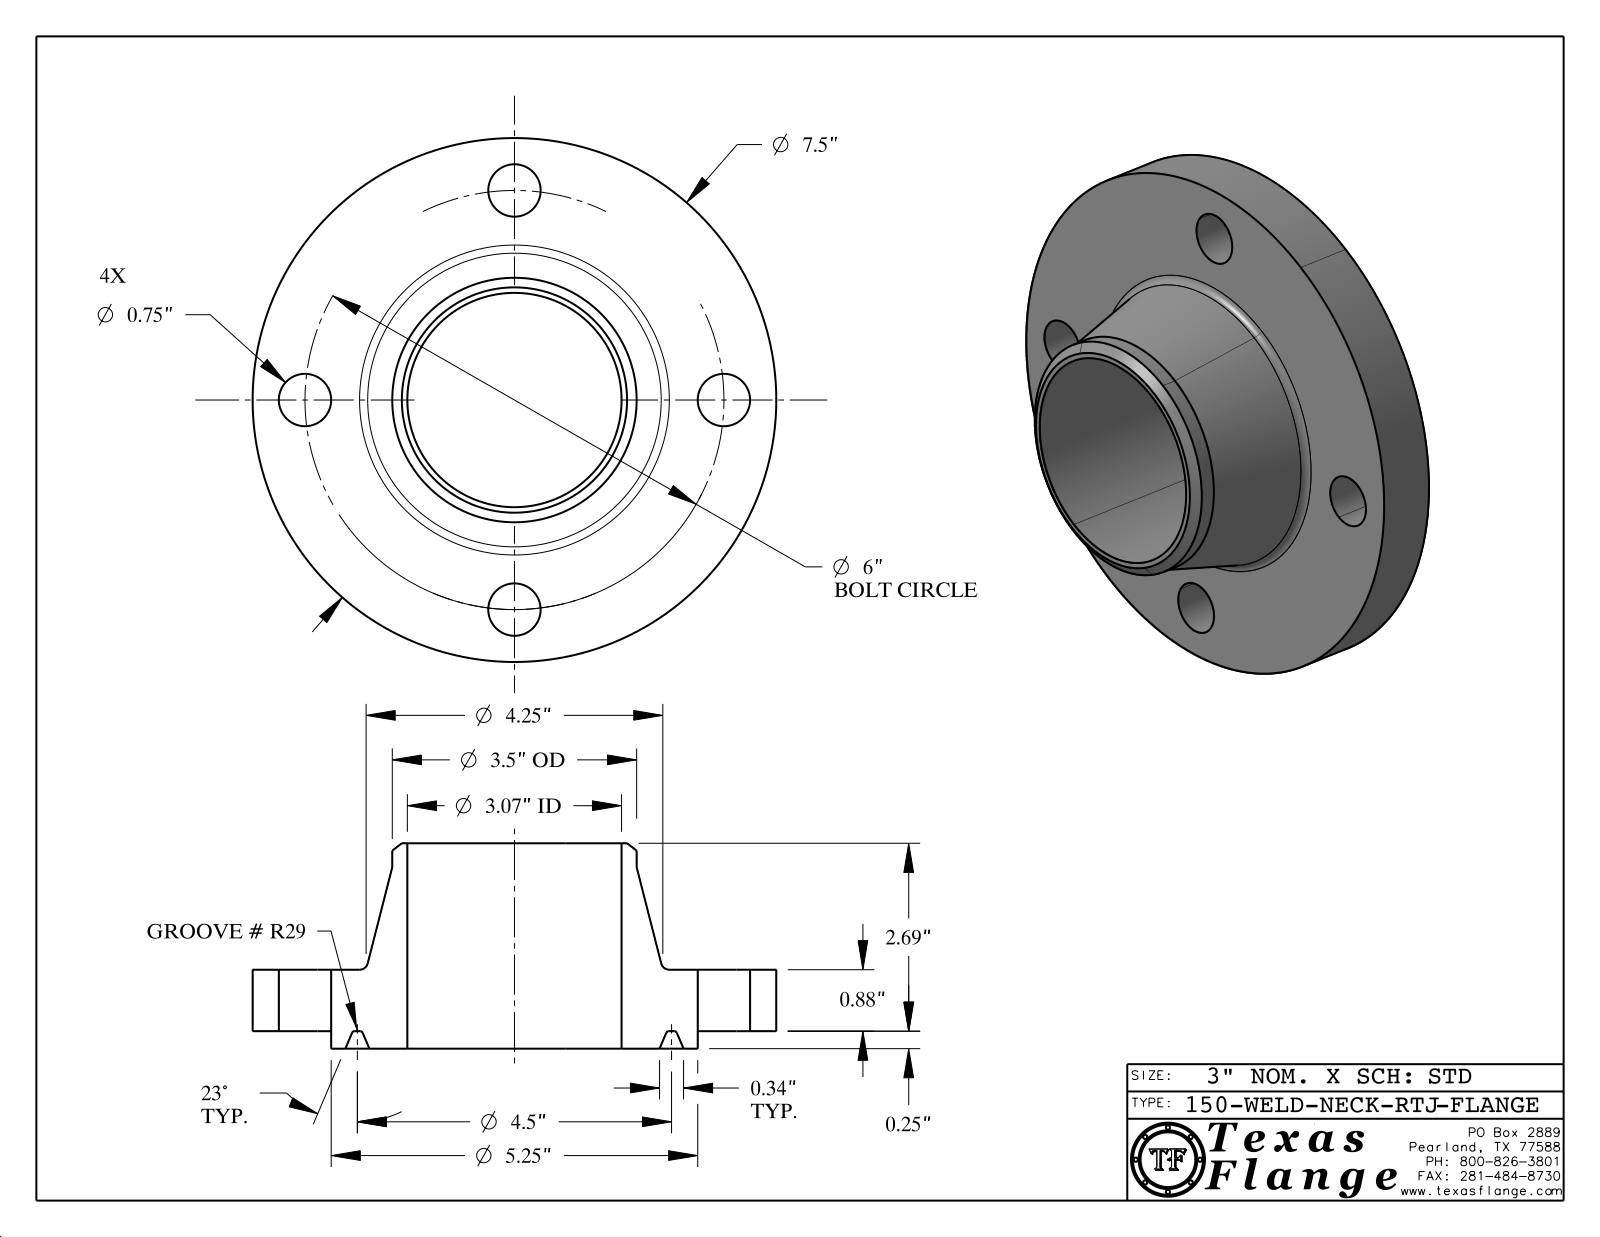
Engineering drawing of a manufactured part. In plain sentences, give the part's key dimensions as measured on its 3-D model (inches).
The part is named "150-WELD-NECK-RTJ". Its 3-D file was written by "CATIA V5 STEP AP214 (AUTOMOTIVE_DESIGN)". It is 1 solid with 421 faces: 371 planar, 36 cylindrical and 14 other. Overall it measures 7.5 by 7.5 by 2.94 inches. Its volume is 40.76 cubic inches and its surface area 152.6 square inches. Round holes: 4 of diameter 0.75, 1 of diameter 0.495, 1 of diameter 3.068. Round bosses or shafts: 8 of diameter 0.03, 1 of diameter 7.5, 1 of diameter 5.25, 1 of diameter 3.5, 1 of diameter 0.39. The main face-to-face distances are 0.88, 0.25, 1.13, 2.94, 2.69, 1.81, 1.125, 0.875, 1.815, 0.148. The hole center spacings are 3, 4.243, 2.296, 5.543, 6.
